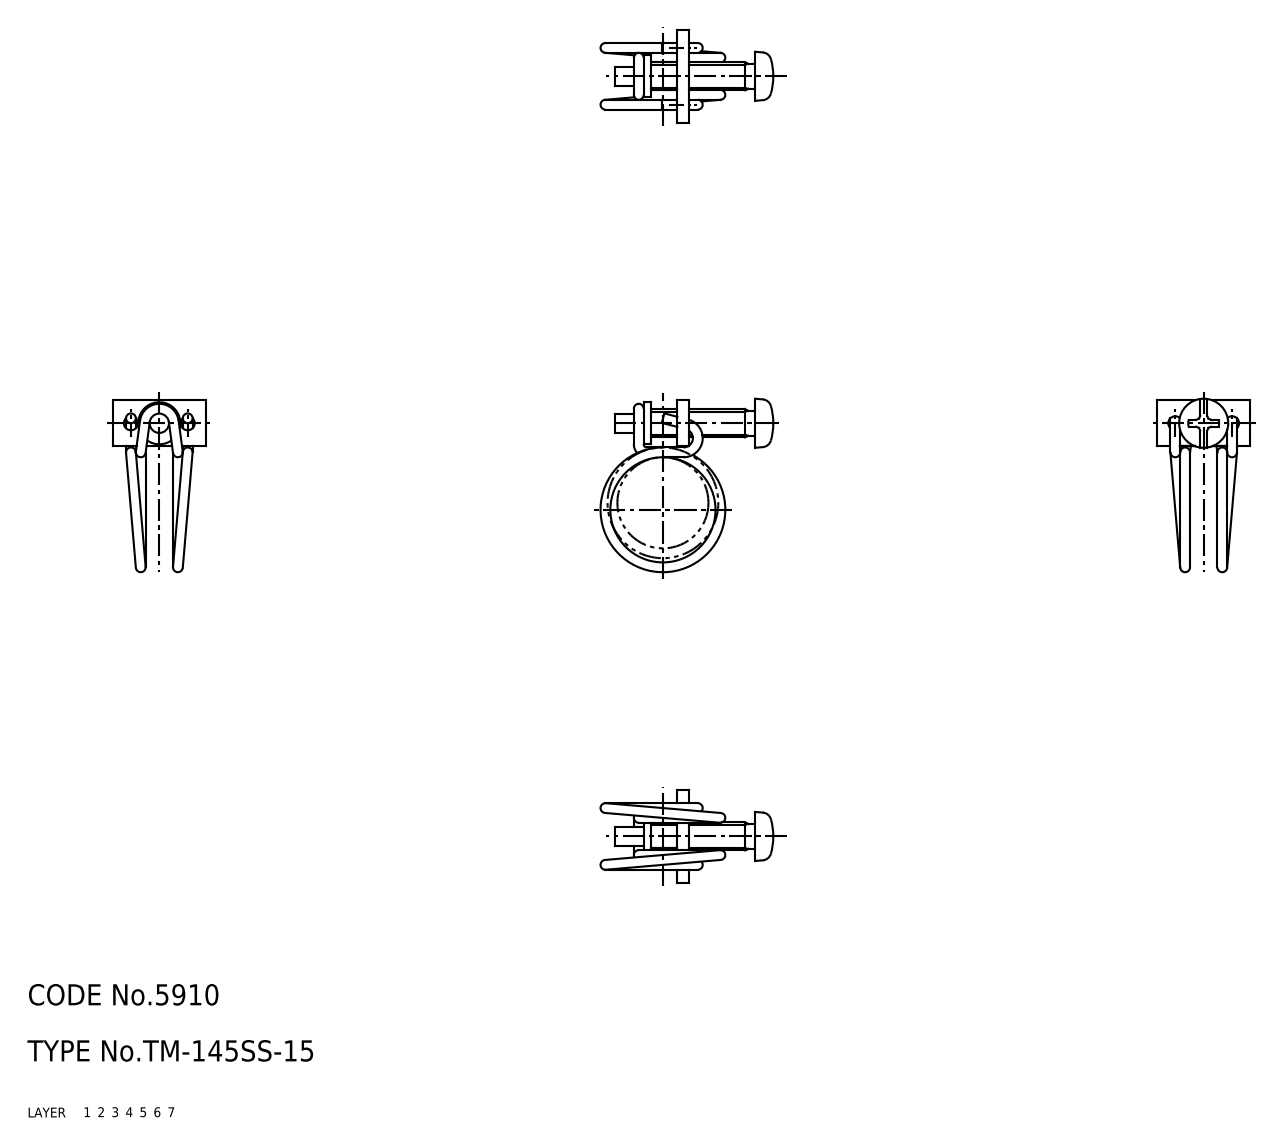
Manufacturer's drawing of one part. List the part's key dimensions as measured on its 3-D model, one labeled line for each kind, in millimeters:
Part name (STEP PRODUCT): 67115108; 67115121; 67115134
STEP written by: CADfix (AUTOMOTIVE_DESIGN)
Units: millimetres
Bodies: 3 solids, 83 faces (0 planar, 0 cylindrical, 83 other)
Overall size (bounding box): 24.75 × 24.6 × 13.3
Volume: 646 mm³ · Surface area: 1 302 mm²
